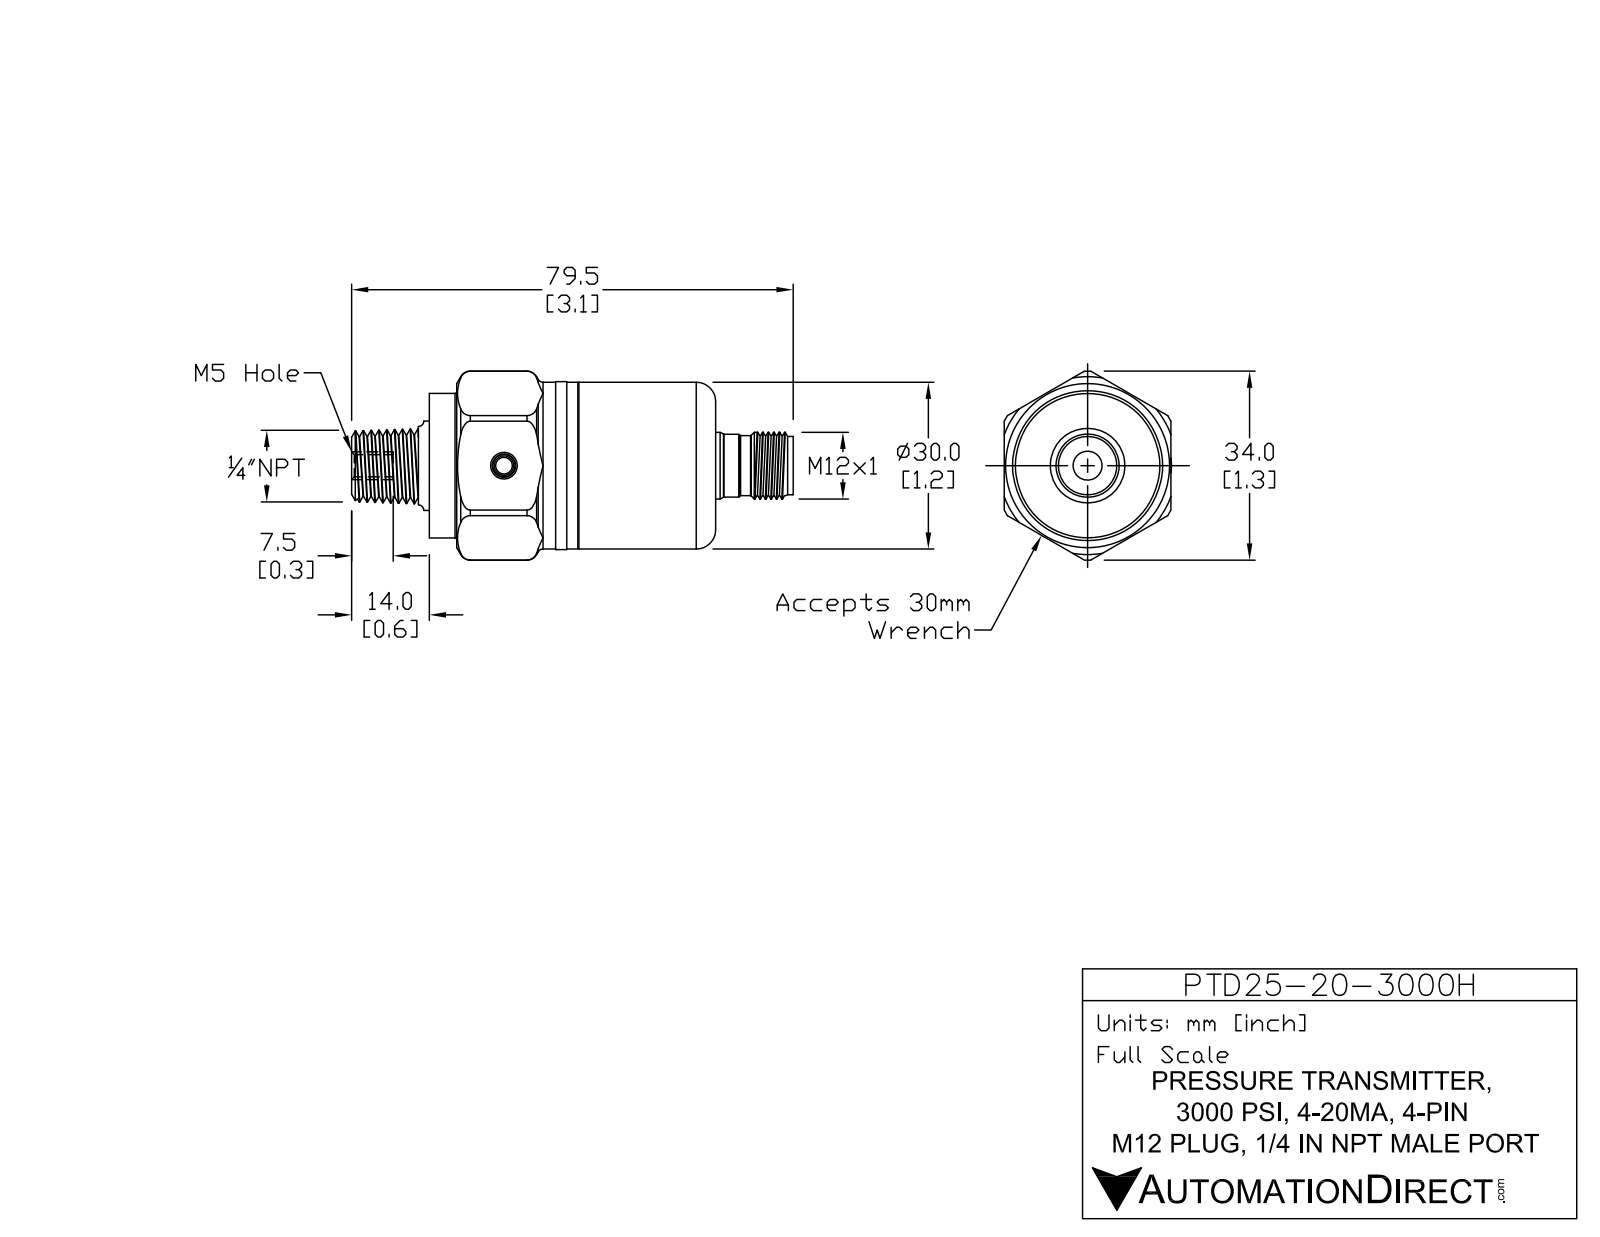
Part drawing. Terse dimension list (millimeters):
name: PTD25-20-3000H
written by: SolidWorks 2017 (AUTOMOTIVE_DESIGN)
unit: mm
bodies: 1 solid, 124 faces (36 planar, 59 cylindrical, 29 other)
size: 79.5 × 33.78 × 31.7
volume: 39 212 mm³; area: 8 088 mm²
holes: 1× ⌀4, 1× ⌀8.5
bosses: 1× ⌀30.05, 1× ⌀30, 1× ⌀25.96, 1× ⌀14, 1× ⌀13.5, 1× ⌀12
rounds: 1× R3.76, 1× R16.95
face distances: 51, 29.98, 30, 48, 3, 65, 17, 14, 30.01, 5.65
